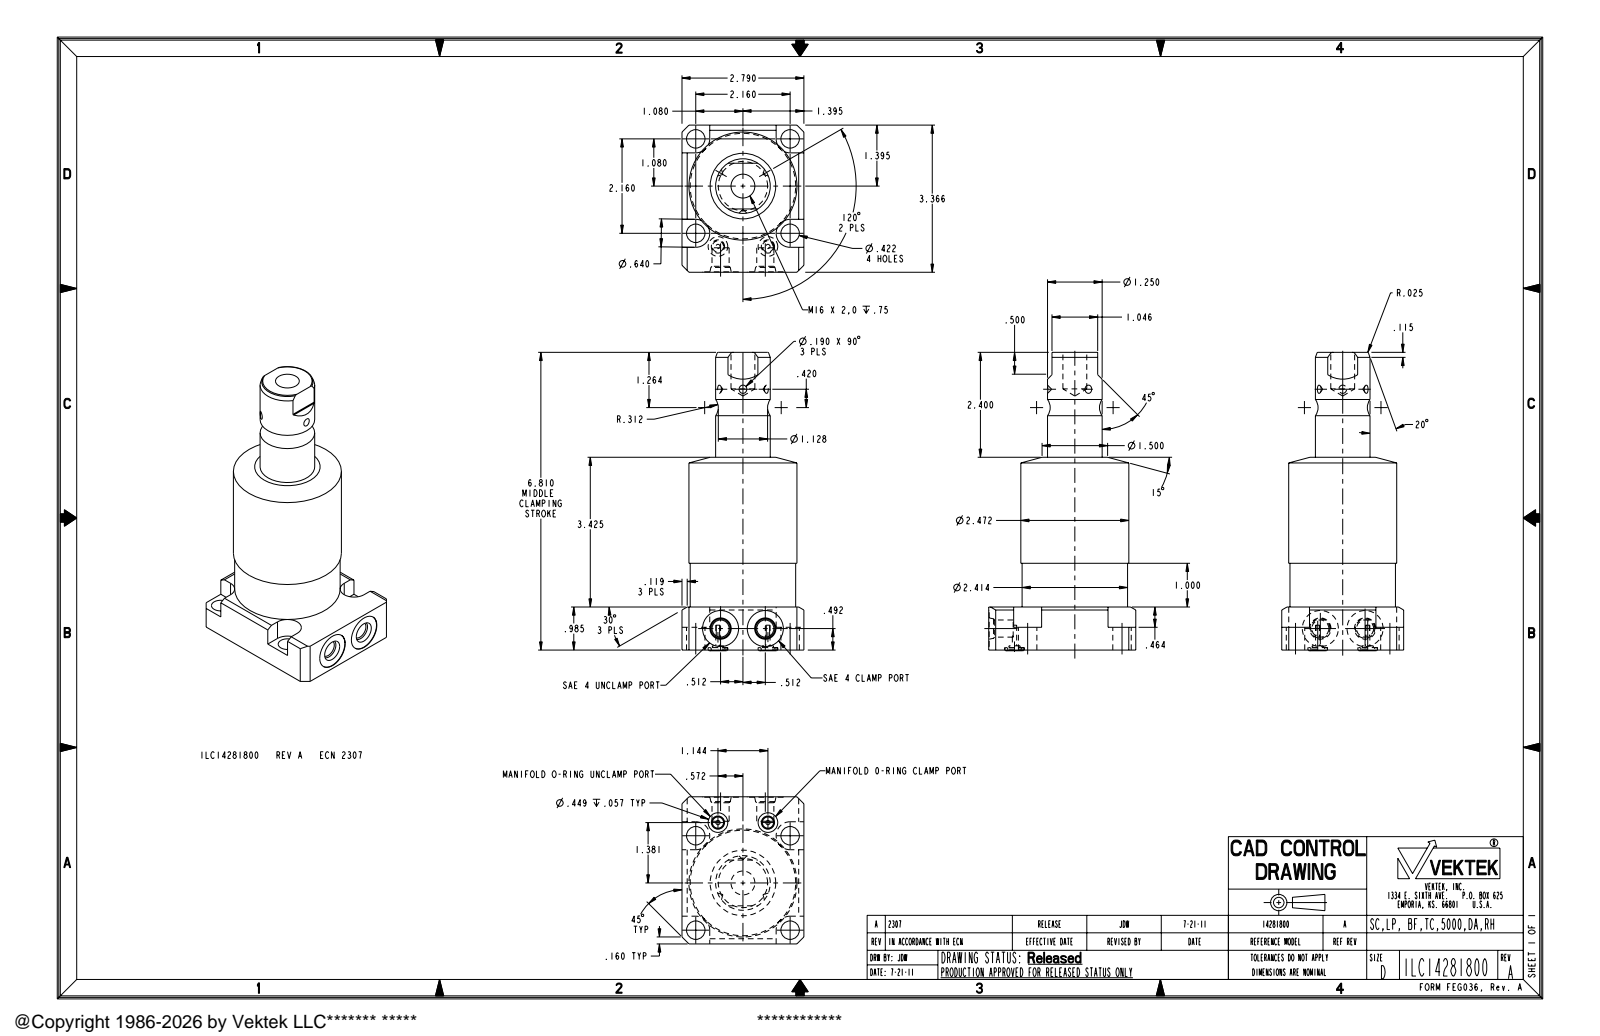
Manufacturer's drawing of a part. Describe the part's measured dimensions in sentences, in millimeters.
The part is named "ILC14281800". Its 3-D file was written by "PRO/ENGINEER BY PARAMETRIC TECHNOLOGY CORPORATION, 2007460 (AUTOMOTIVE_DESIGN_CC2)". It is 1 solid with 125 faces: 47 planar, 46 cylindrical and 32 other. Overall it measures 173.4 by 85.5 by 70.9 millimeters. Its volume is 436 700 cubic millimeters and its surface area 46 230 square millimeters. Round holes: 4 of diameter 10.7, 2 of diameter 2.5, 2 of diameter 6.5, 2 of diameter 10, 2 of diameter 11.4, 2 of diameter 21, 1 of diameter 13.9. Round bosses or shafts: 1 of diameter 62.8, 1 of diameter 61.3, 1 of diameter 31.8. Partial cylindrical surfaces (rounded edges, fillets, slot ends): 4 of radius 8.1, 2 of radius 0.8. The main face-to-face distances are 25, 70.9, 85.5, 11.8, 13.2, 148, 159.7, 173, 85.2, 6. The hole center spacings are 38.8, 54.9, 15, 38, 42.6, 63.8, 75.3, 77.6.
